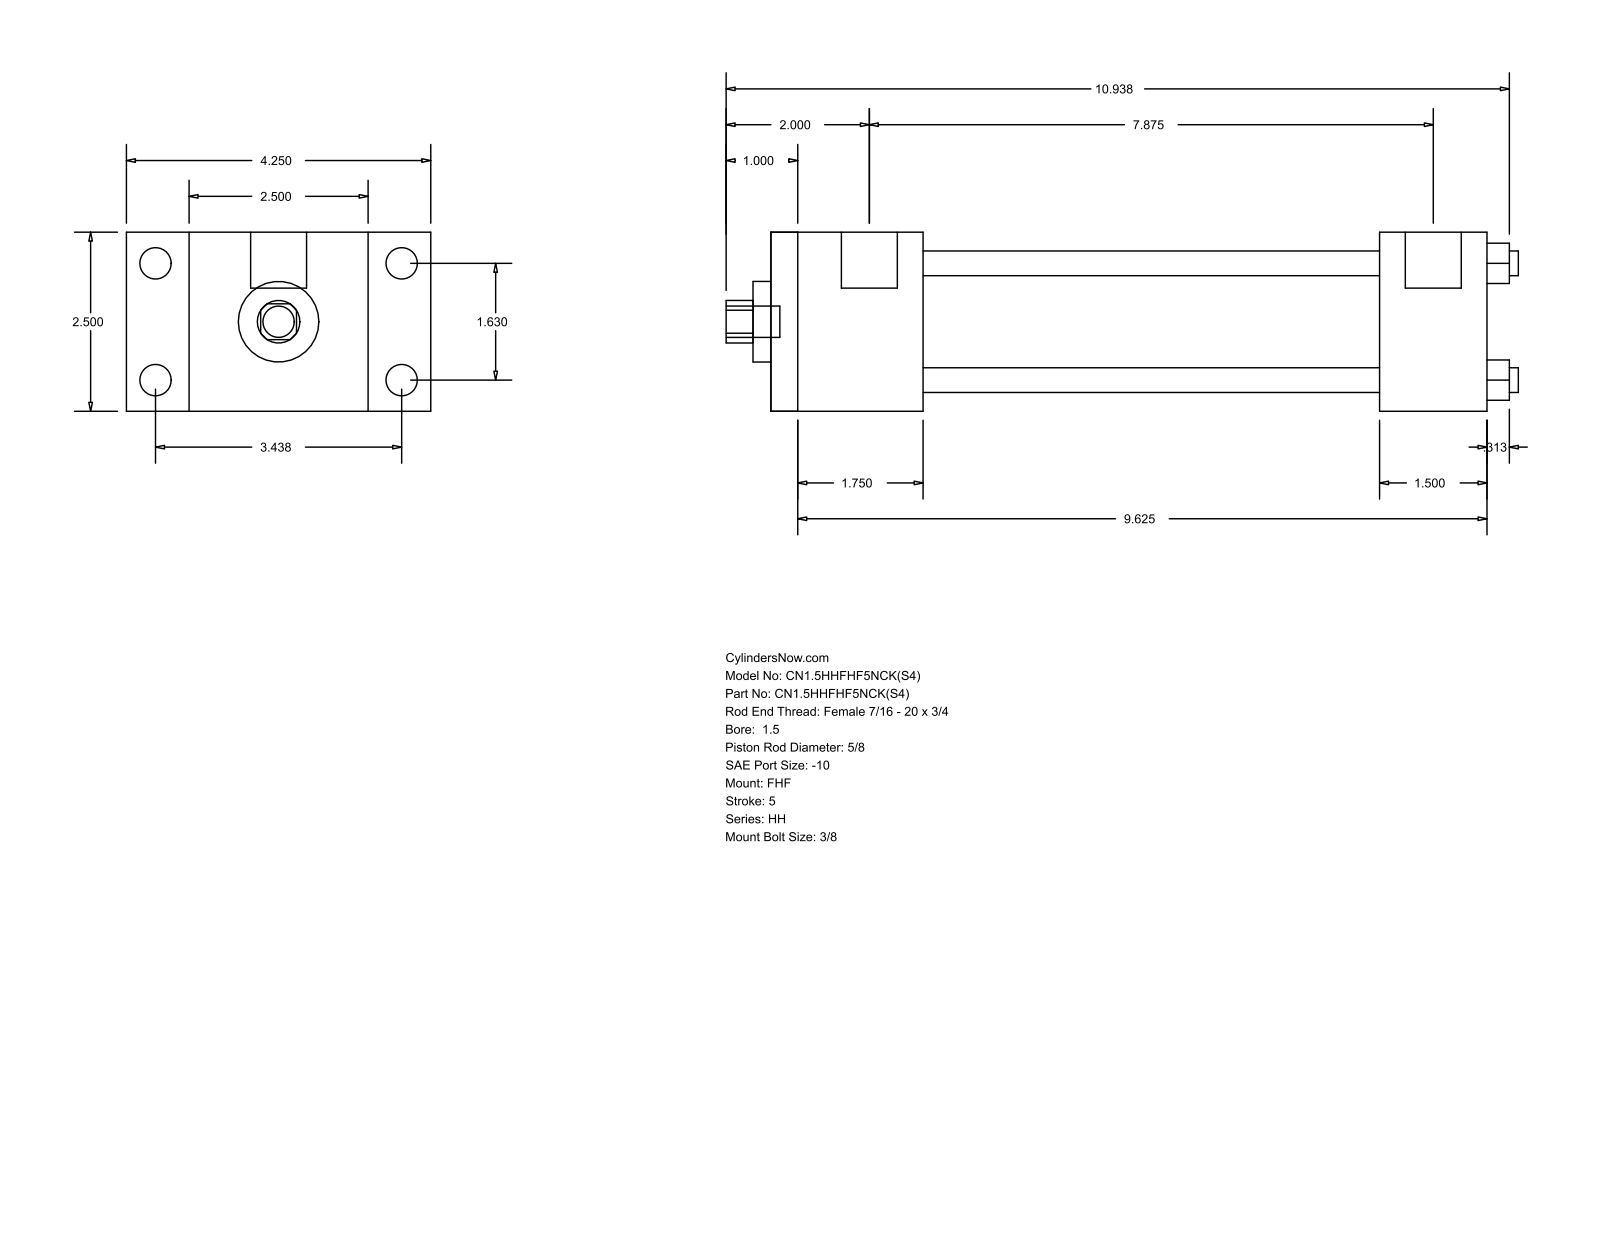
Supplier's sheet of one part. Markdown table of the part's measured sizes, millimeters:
| quantity | value |
| --- | --- |
| part name | HH_FHF__0150_0.625 |
| STEP written by | GSSL Pune (CONFIG_CONTROL_DESIGN) |
| units | millimeters |
| bodies | 0 solids, 88 faces (60 planar, 28 cylindrical, 0 other) |
| overall size | 280.99 × 107.95 × 63.5 |
| round holes (diameter × count) | 8.76 × 4, 15.88 × 1, 28.57 × 1, 44.45 × 1 |
| round bosses / shafts (diameter × count) | 11.13 × 4, 5.56 × 4, 19.84 × 2, 11.11 × 1 |
| partial cylindrical surfaces (radius × count) | 7.54 × 1 |
| main face-to-face distances | 63.5, 22.23, 85.73, 53.97, 107.96, 254, 200.03, 38.1, 215.9, 161.93 |
| hole center spacings | 29.27, 41.4, 58.55 |
